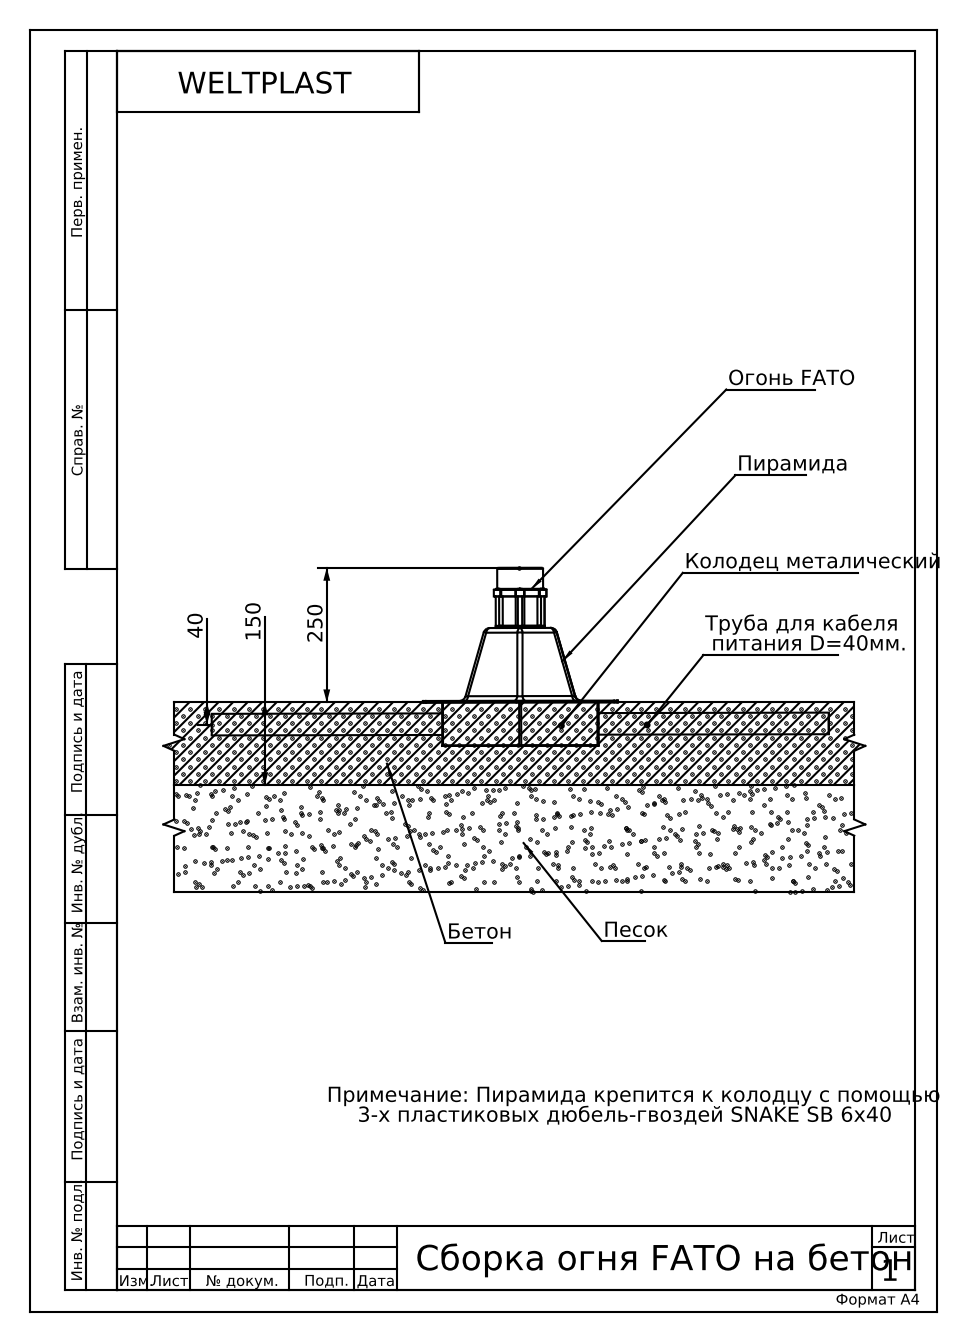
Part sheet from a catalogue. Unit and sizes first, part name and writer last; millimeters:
Units: millimetres
Overall size (bounding box): 1013.06 × 601.51 × 331
Round holes (diameter × count): ⌀4.4 ×7, ⌀4.5 ×6, ⌀5 ×5, ⌀5.3 ×4, ⌀4 ×3, ⌀4.2 ×2, ⌀12.6 ×2, ⌀20.25 ×2, ⌀26 ×2, ⌀40 ×2, ⌀12 ×1, ⌀70 ×1
Round bosses / shafts (diameter × count): ⌀7.6 ×6, ⌀5 ×3, ⌀4 ×3, ⌀40 ×2, ⌀21.5 ×2, ⌀19.7 ×2, ⌀15 ×2, ⌀85 ×1
Partial cylindrical surfaces — rounded edges, fillets, slot ends (radius × count): R2 ×28, R12 ×26, R5 ×24, R4.5 ×18, R1.5 ×14, R1 ×13, R3 ×12, R10 ×12
Main face-to-face distances: 3, 1.5, 81.5, 80, 84.5, 83, 287.15, 287.48, 286.71, 64.5
Hole centre spacings: 47.5, 42.28, 54.13, 82.28, 48.09, 55.84, 41.18, 82.27
Volume: 1 709 000 mm³ · Surface area: 1 006 000 mm²
Bodies: 40 solids, 1507 faces (620 planar, 669 cylindrical, 218 other)
Part name (STEP PRODUCT): Провод 25; Конектор мама Сборка 1; Сборка фонаря байонет; конектор мама защёлка (+8 more)
STEP written by: SolidWorks 2018 (AUTOMOTIVE_DESIGN)
